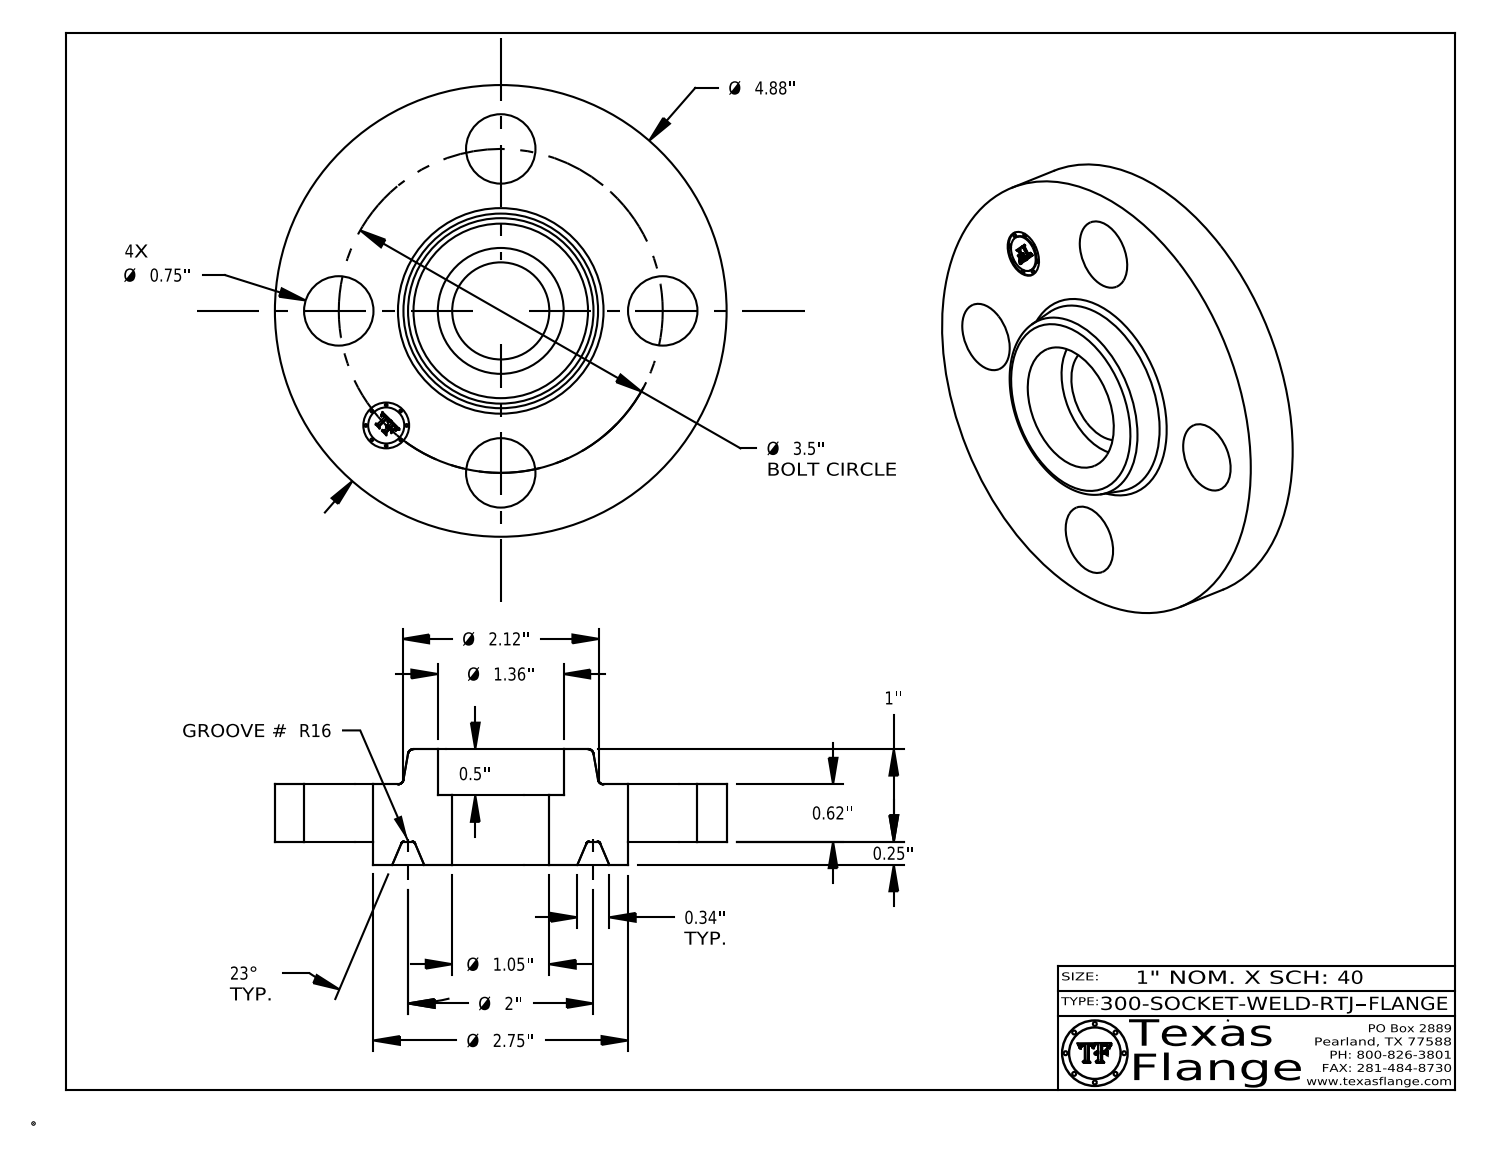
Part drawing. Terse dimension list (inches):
name: 300-SOCKET-WELD-RTJ
written by: CATIA V5 STEP AP214 (AUTOMOTIVE_DESIGN)
unit: in
bodies: 1 solid, 422 faces (372 planar, 36 cylindrical, 14 other)
size: 4.88 × 4.88 × 1.25
volume: 11.5 in³; area: 58.21 in²
holes: 4× ⌀0.75, 1× ⌀0.495, 1× ⌀1.049, 1× ⌀1.36
bosses: 8× ⌀0.03, 1× ⌀4.88, 1× ⌀2.75, 1× ⌀0.39
face distances: 0.62, 0.25, 0.87, 1.25, 1, 0.38, 0.5, 0.75, 0.12, 0.105
hole spacings: 1.75, 2.475, 1.339, 3.233, 3.5
